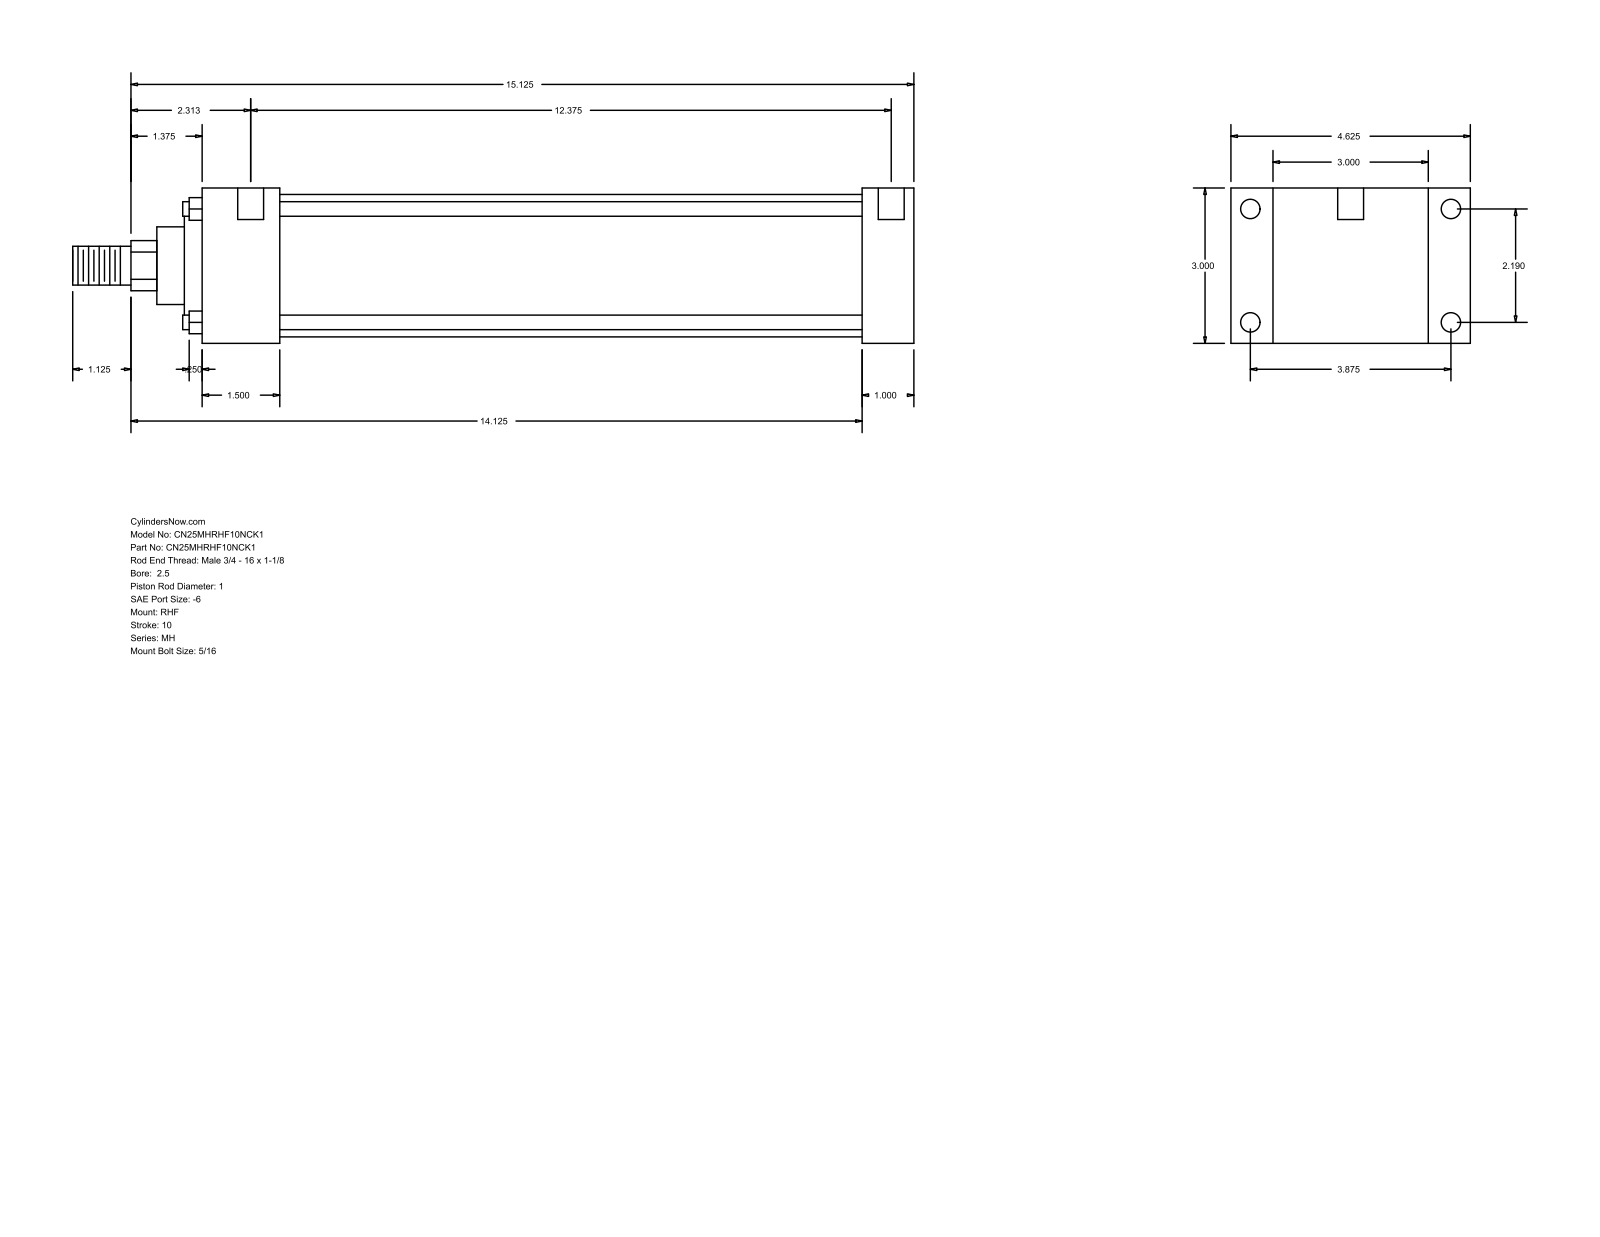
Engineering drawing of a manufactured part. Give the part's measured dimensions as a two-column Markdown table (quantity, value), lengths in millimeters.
| quantity | value |
| --- | --- |
| part name | MH_RHF__0250_1 |
| STEP written by | GSSL Pune (CONFIG_CONTROL_DESIGN) |
| units | millimeters |
| bodies | 0 solids, 90 faces (61 planar, 29 cylindrical, 0 other) |
| overall size | 412.75 × 117.47 × 76.2 |
| round holes (diameter × count) | 5.56 × 4, 9.53 × 4, 12.7 × 2 |
| round bosses / shafts (diameter × count) | 7.14 × 4, 69.85 × 1, 60.33 × 1, 38.1 × 1, 25.4 × 1, 19.05 × 1 |
| partial cylindrical surfaces (radius × count) | 12.29 × 1 |
| main face-to-face distances | 76.2, 25.41, 20.64, 96.84, 323.85, 349.26, 117.48, 38.11, 285.74, 311.15 |
| hole center spacings | 55.62, 98.42, 113.05, 322.26, 3.18, 4.76, 314.32, 317.5 |
